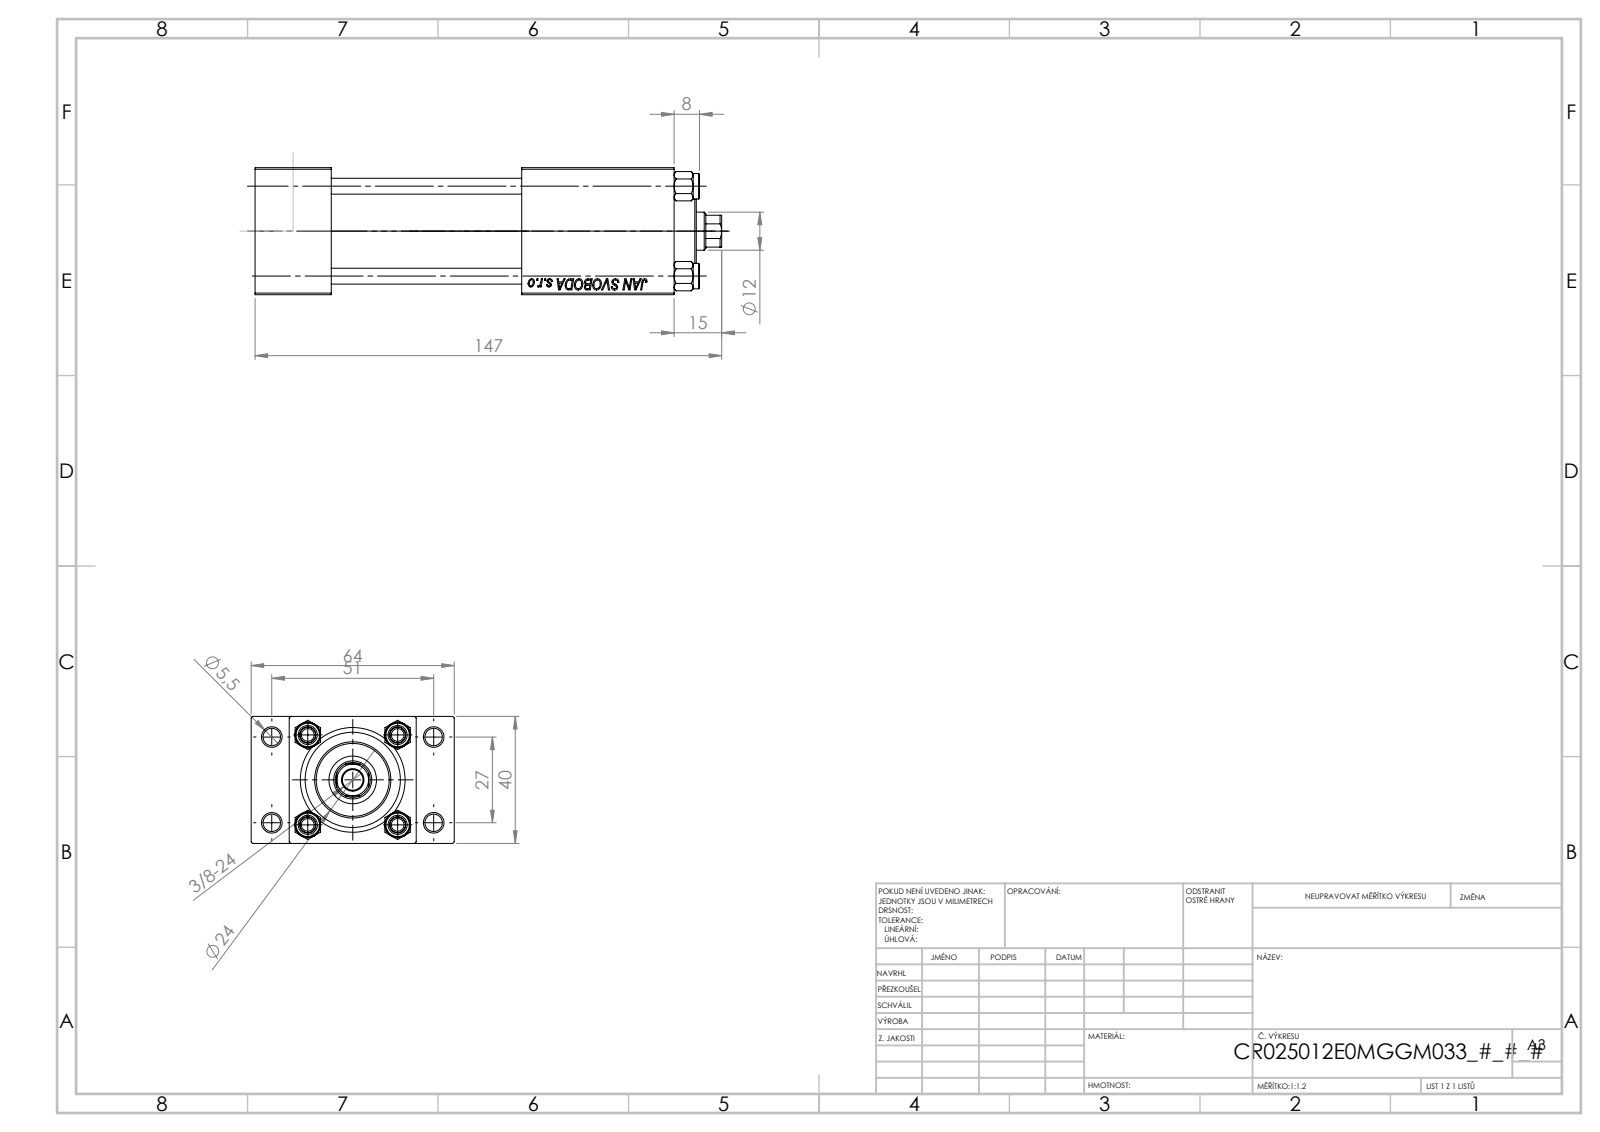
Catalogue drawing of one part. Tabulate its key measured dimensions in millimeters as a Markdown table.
| quantity | value |
| --- | --- |
| part name | NUT_M5_E; V215CR_E_Body; V215_VC_A; V215CR_VCP_E (+1 more) |
| STEP written by | SolidWorks 2019 (CONFIG_CONTROL_DESIGN) |
| units | millimeters |
| bodies | 11 solids, 1136 faces (497 planar, 87 cylindrical, 552 other) |
| overall size | 147 × 64 × 40 |
| volume | 169 837 mm³ |
| surface area | 65 699 mm² |
| round holes (diameter × count) | 5 × 4, 5.5 × 4, 20 × 3, 7 × 2, 13.16 × 2, 6.5 × 1, 12 × 1, 15 × 1, 25 × 1, 30 × 1 |
| round bosses / shafts (diameter × count) | 8 × 4, 31 × 1, 24 × 1 |
| partial cylindrical surfaces (radius × count) | 5.5 × 1 |
| main face-to-face distances | 40, 24, 12, 52, 132, 108, 103.3, 79.3, 28.7, 64 |
| hole center spacings | 11.37, 20.01, 28.3, 28.85, 29.89, 39.66, 48.34, 27 |
